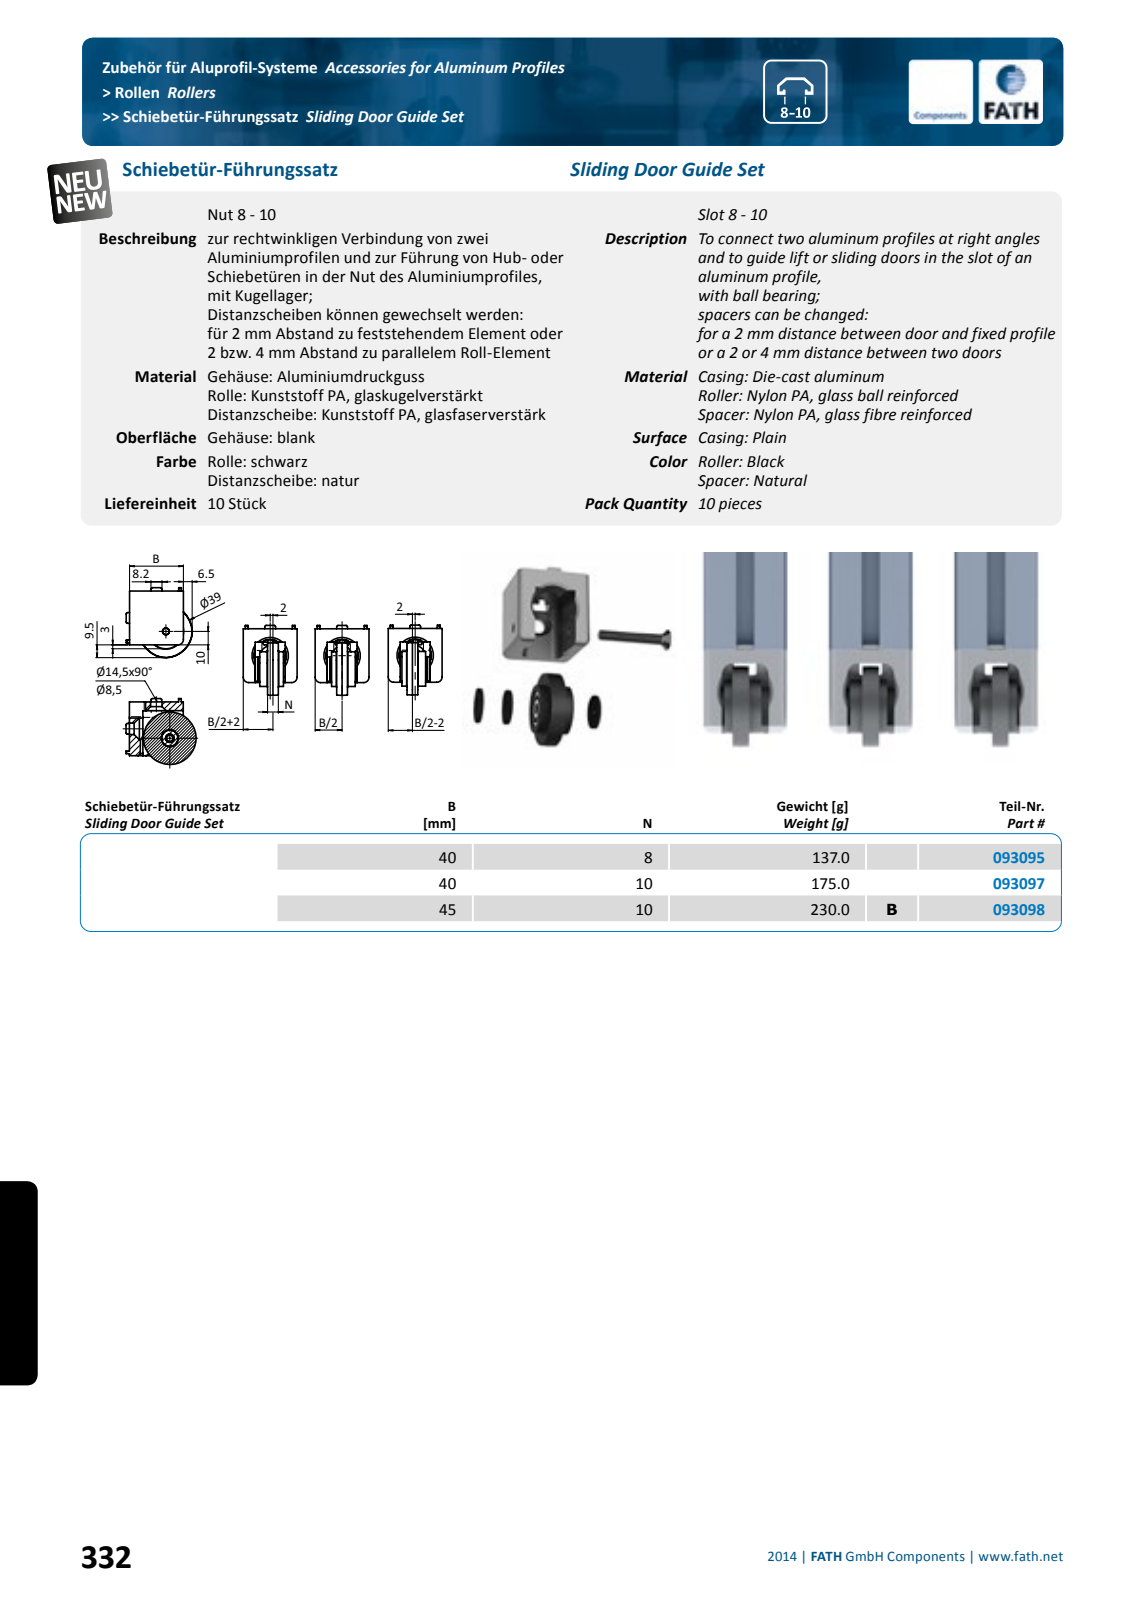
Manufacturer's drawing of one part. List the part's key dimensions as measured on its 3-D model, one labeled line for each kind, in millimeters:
Part name (STEP PRODUCT): fath_093095_1; fath_093095_2; fath_093095_3; fath_093095_4 (+5 more)
STEP written by: Spatial InterOp 3D (automotive_design)
Units: millimetres
Bodies: 9 solids, 284 faces (83 planar, 118 cylindrical, 83 other)
Overall size (bounding box): 52 × 49 × 40
Volume: 50 549 mm³ · Surface area: 22 044 mm²
Round holes (diameter × count): ⌀8.5 ×2, ⌀16.3 ×2, ⌀5 ×1, ⌀6 ×1, ⌀6.3 ×1, ⌀6.4 ×1, ⌀6.6 ×1, ⌀12.7 ×1, ⌀15.1 ×1, ⌀19 ×1
Round bosses / shafts (diameter × count): ⌀25.8 ×1, ⌀18 ×1, ⌀12 ×1, ⌀9.9 ×1
Partial cylindrical surfaces — rounded edges, fillets, slot ends (radius × count): R1 ×24, R0.5 ×8, R4 ×5, R5 ×5, R7.9 ×1
Main face-to-face distances: 40, 2, 8.7, 31.3, 8, 10.7, 29.3, 20.6, 7.25, 24.05
